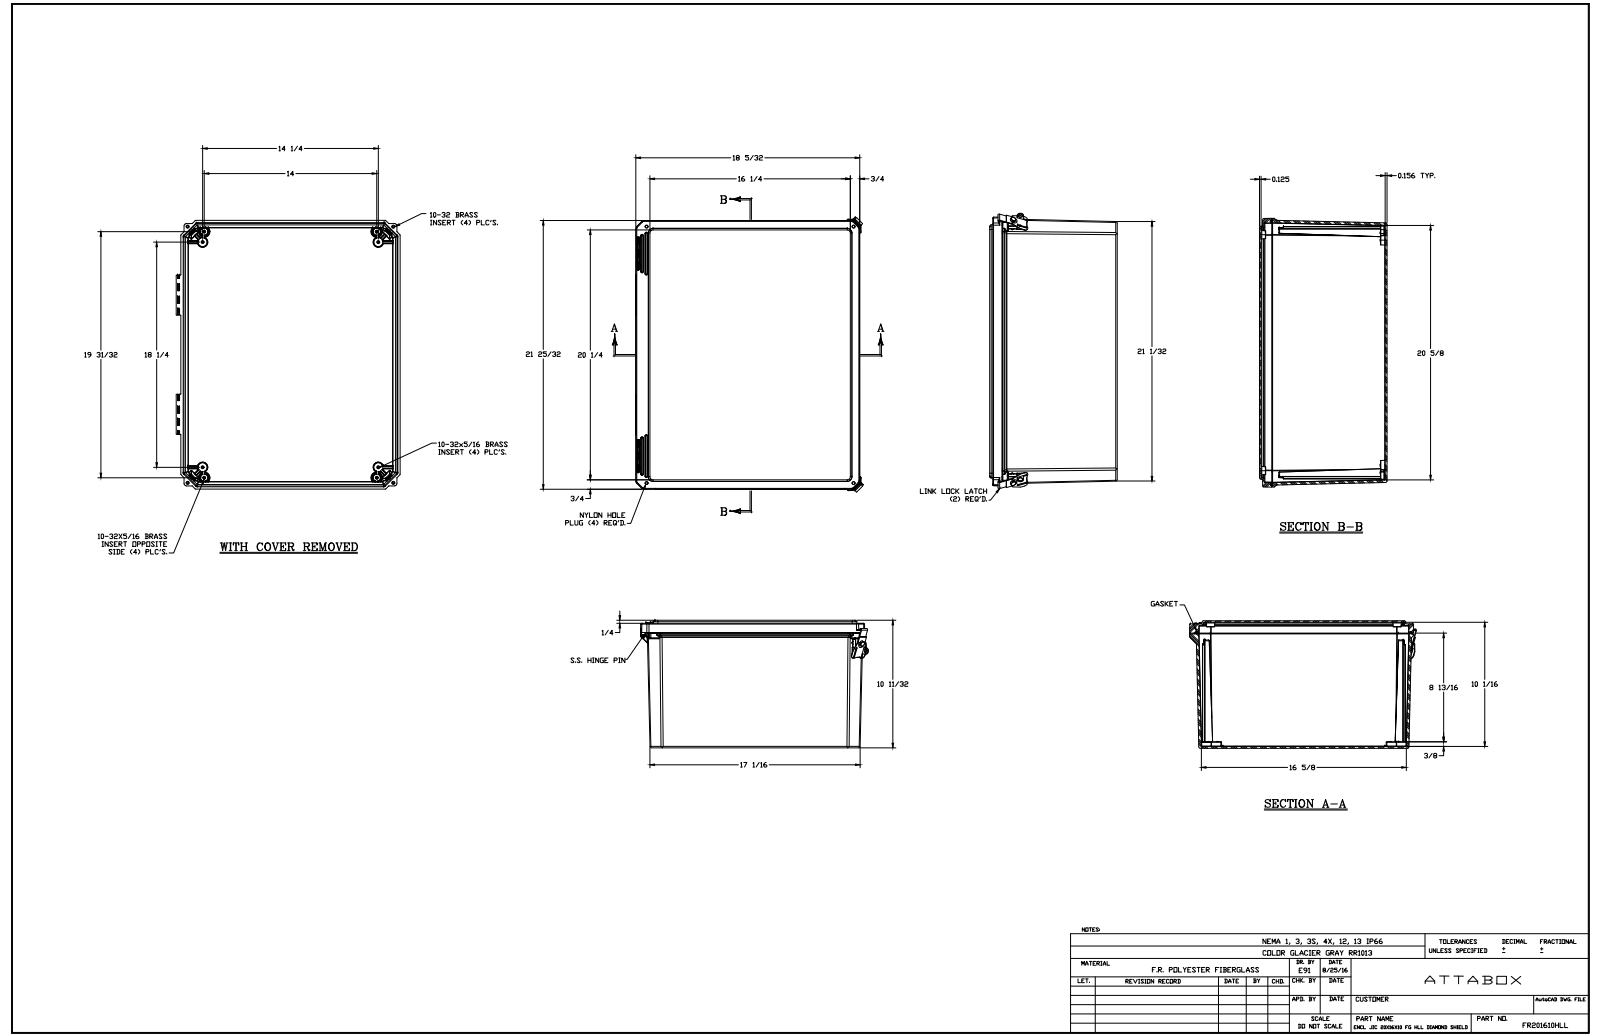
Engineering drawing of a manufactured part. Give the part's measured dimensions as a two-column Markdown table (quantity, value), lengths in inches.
| quantity | value |
| --- | --- |
| part name | FR201610HLL |
| STEP written by | SolidWorks 2018 (AUTOMOTIVE_DESIGN) |
| units | inches |
| bodies | 37 solids, 2342 faces (822 planar, 924 cylindrical, 596 other) |
| overall size | 22.578 × 18.561 × 10.338 |
| volume | 285.8 in³ |
| surface area | 3 208 in² |
| round holes (diameter × count) | 0.156 × 16, 0.152 × 8, 0.098 × 4, 0.15 × 4, 0.252 × 4, 0.253 × 4, 0.05 × 2, 0.12 × 2, 0.137 × 2, 0.219 × 2, 0.227 × 2, 0.313 × 2 |
| round bosses / shafts (diameter × count) | 0.246 × 16, 0.209 × 4, 0.2 × 4, 0.6 × 2, 0.435 × 2, 0.135 × 2, 0.05 × 2, 0.135 × 1 |
| partial cylindrical surfaces (radius × count) | 0.01 × 197, 0.005 × 88, 0.02 × 49, 0.03 × 44, 0.125 × 34, 0.039 × 28, 0.03 × 24, 0.09 × 24 |
| main face-to-face distances | 0.125, 0.156, 10.182, 10.338, 10.213, 10.057, 0.212, 0.21, 0.25, 0.125 |
| hole center spacings | 0.862, 14.151, 15.572, 19.104, 19.561, 1.456, 1.795, 1.795 |
